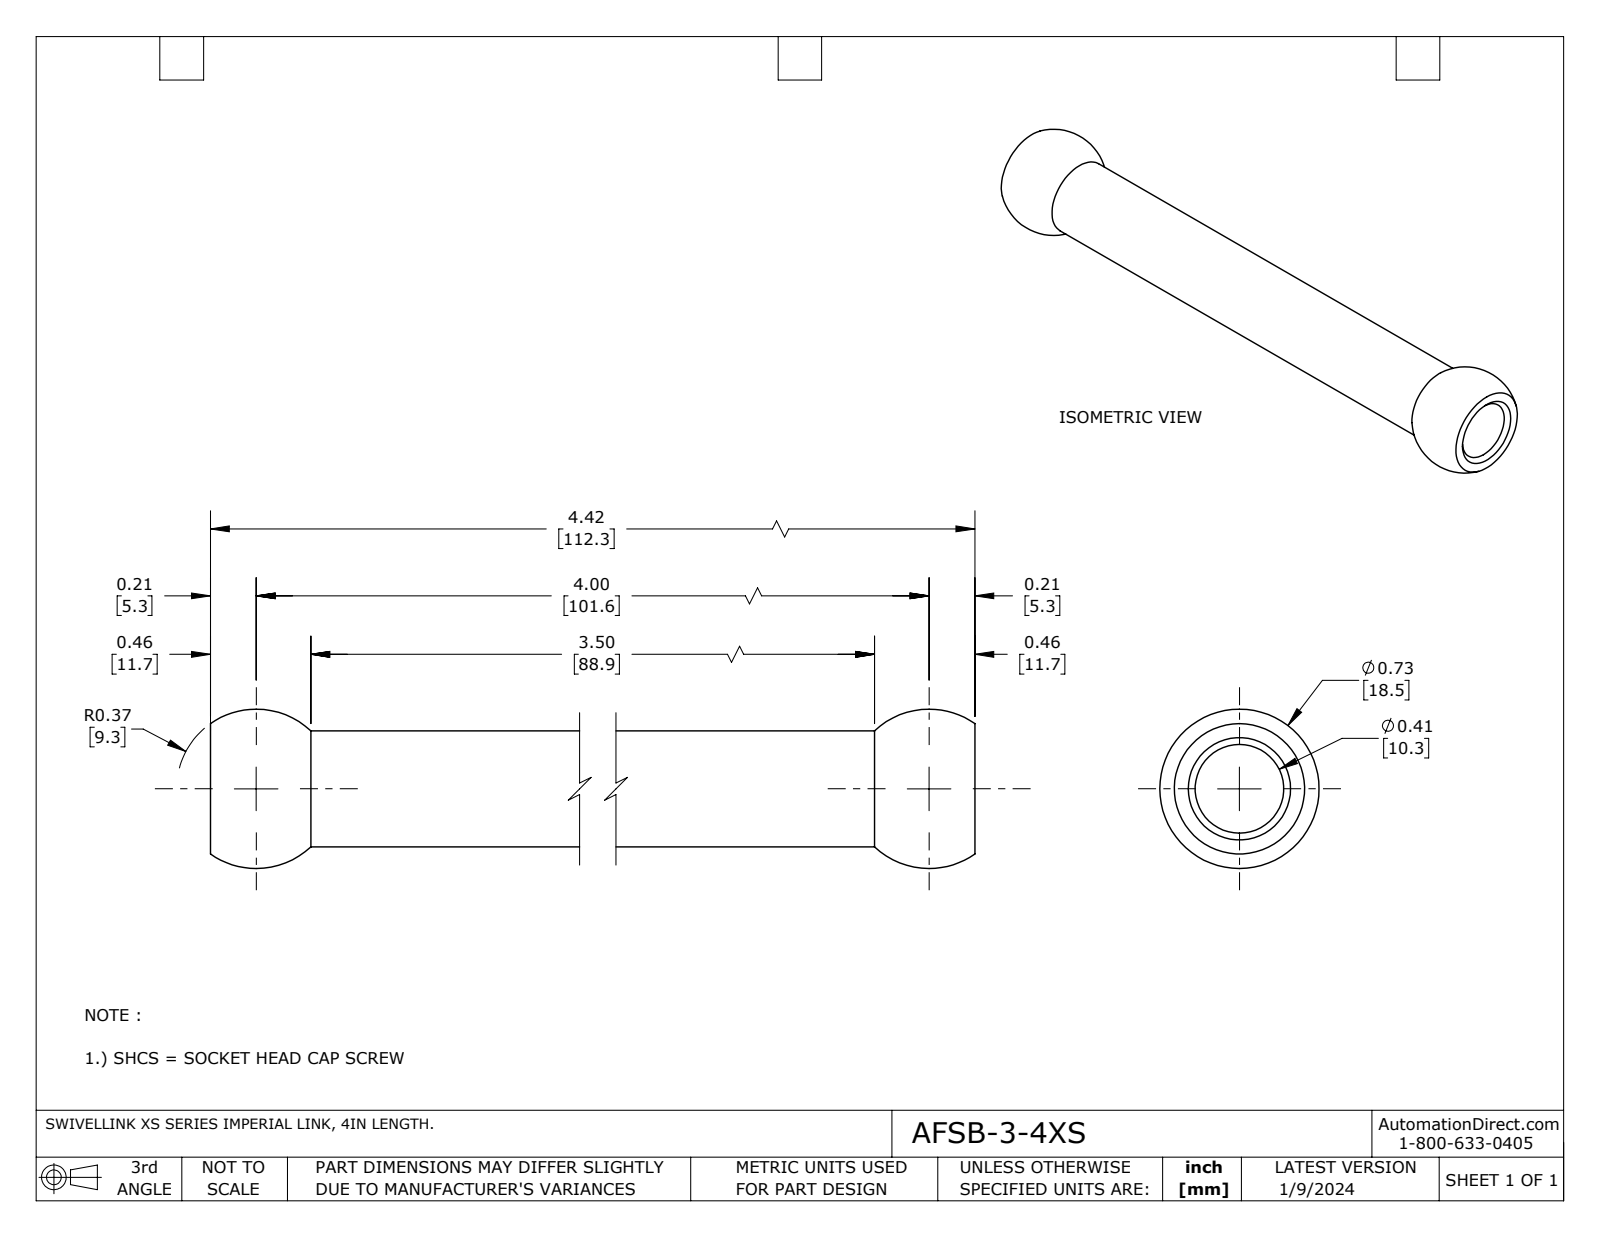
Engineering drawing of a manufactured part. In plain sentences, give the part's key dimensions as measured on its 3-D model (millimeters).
The part is named "AFSB-3-4XS". Its 3-D file was written by "SolidWorks 2023 (AUTOMOTIVE_DESIGN)". It is 2 solids with 10 faces: 2 planar, 2 cylindrical and 6 other. Overall it measures 120.1 by 15.2 by 15.2 millimeters. Its volume is 22 450 cubic millimeters and its surface area 8 368 square millimeters. Round bosses or shafts: 1 of diameter 13.5, 1 of diameter 10.3. The main face-to-face distances are 112.3.
